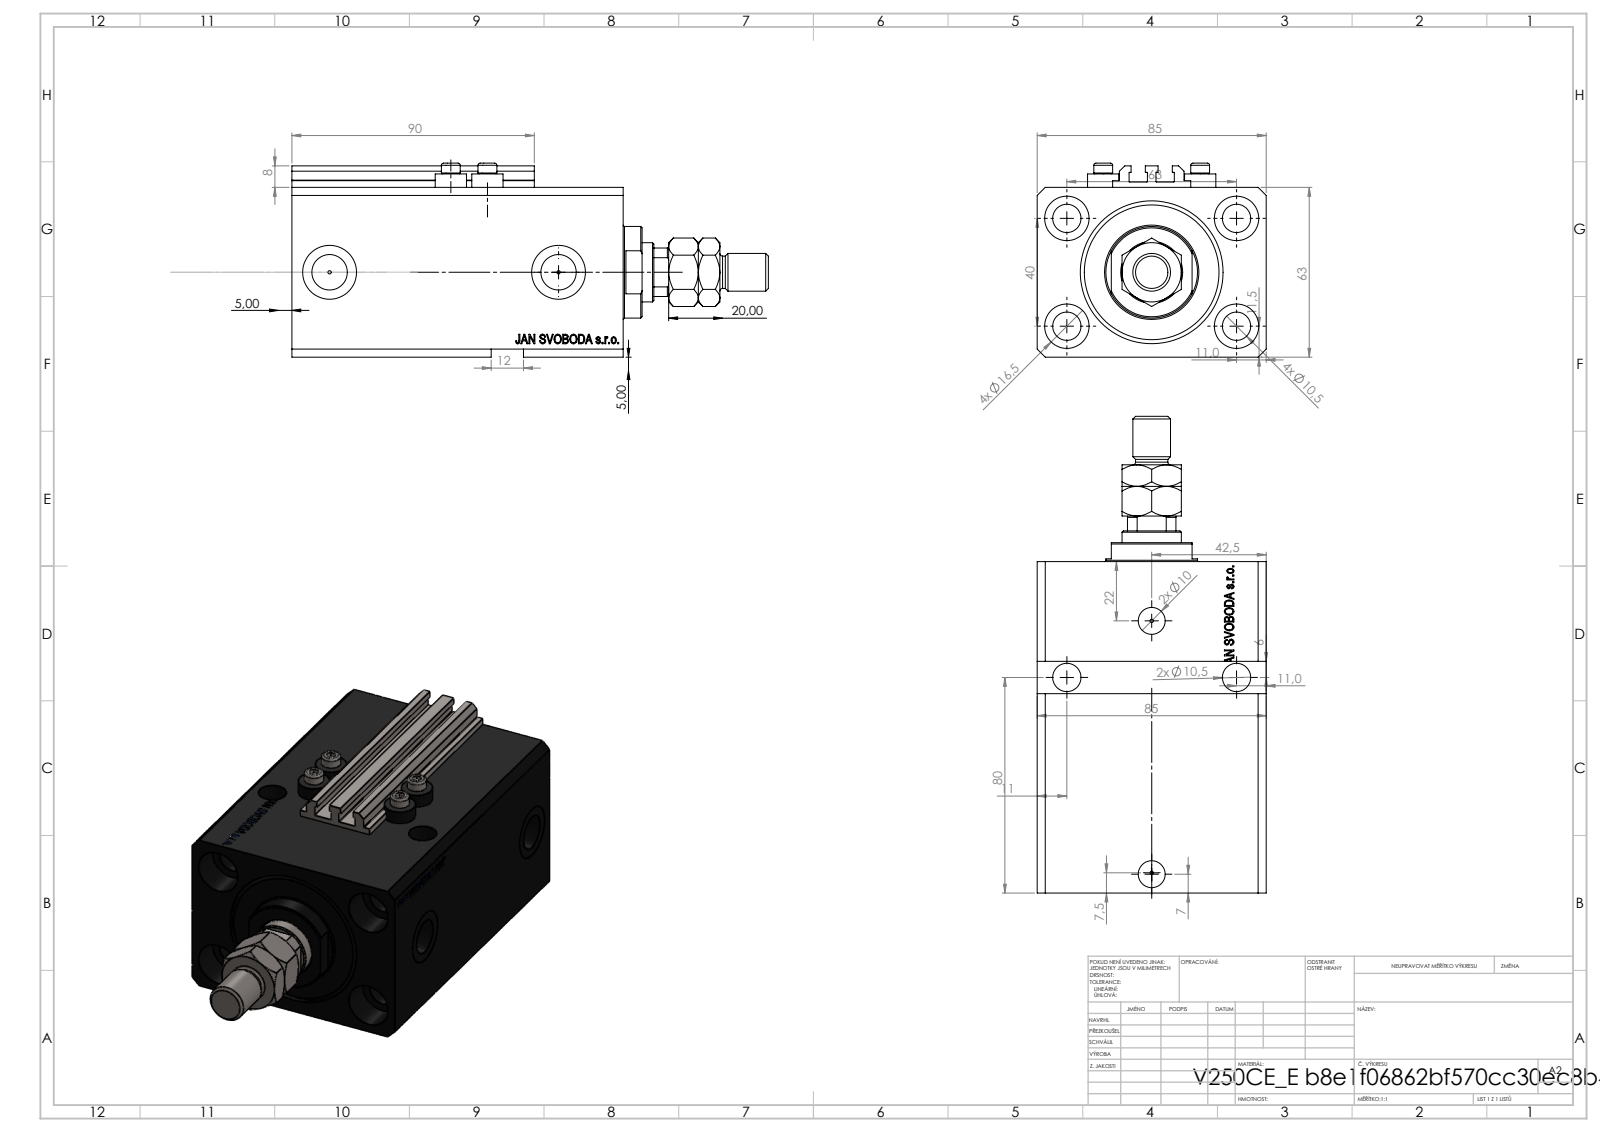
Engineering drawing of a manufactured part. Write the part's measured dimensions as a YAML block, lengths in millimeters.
part_name: "V250CE_C_VCP; MTA; V250CE_E_Body; ALLEN BOLT V250CE (+1 more)"
step_written_by: "SolidWorks 2019 (CONFIG_CONTROL_DESIGN)"
units: millimeters
bodies: {solids: 9, faces: 1172, planar: 554, cylindrical: 162, other: 456}
overall_size: [177, 85, 72]
volume: 563556
surface_area: 123526
round_holes:
  - {diameter: 10.5, count: 8}
  - {diameter: 1.25, count: 4}
  - {diameter: 4, count: 4}
  - {diameter: 16.5, count: 4}
  - {diameter: 10, count: 2}
  - {diameter: 13.16, count: 2}
  - {diameter: 20, count: 2}
  - {diameter: 12.5, count: 1}
  - {diameter: 22, count: 1}
  - {diameter: 40, count: 1}
  - {diameter: 53, count: 1}
round_bosses_or_shafts:
  - {diameter: 11.6, count: 4}
  - {diameter: 7, count: 4}
  - {diameter: 34, count: 1}
  - {diameter: 14, count: 1}
  - {diameter: 12, count: 1}
partial_cylinders:
  - {radius: 0.2, count: 10}
  - {radius: 10.5, count: 1}
face_to_face_distances: [63, 85, 17, 123, 106, 11.4, 94.6, 111.6, 3, 65]
hole_center_spacings: [37.31, 63, 13.6, 15.4, 24.96, 27.54, 33.62, 36]
